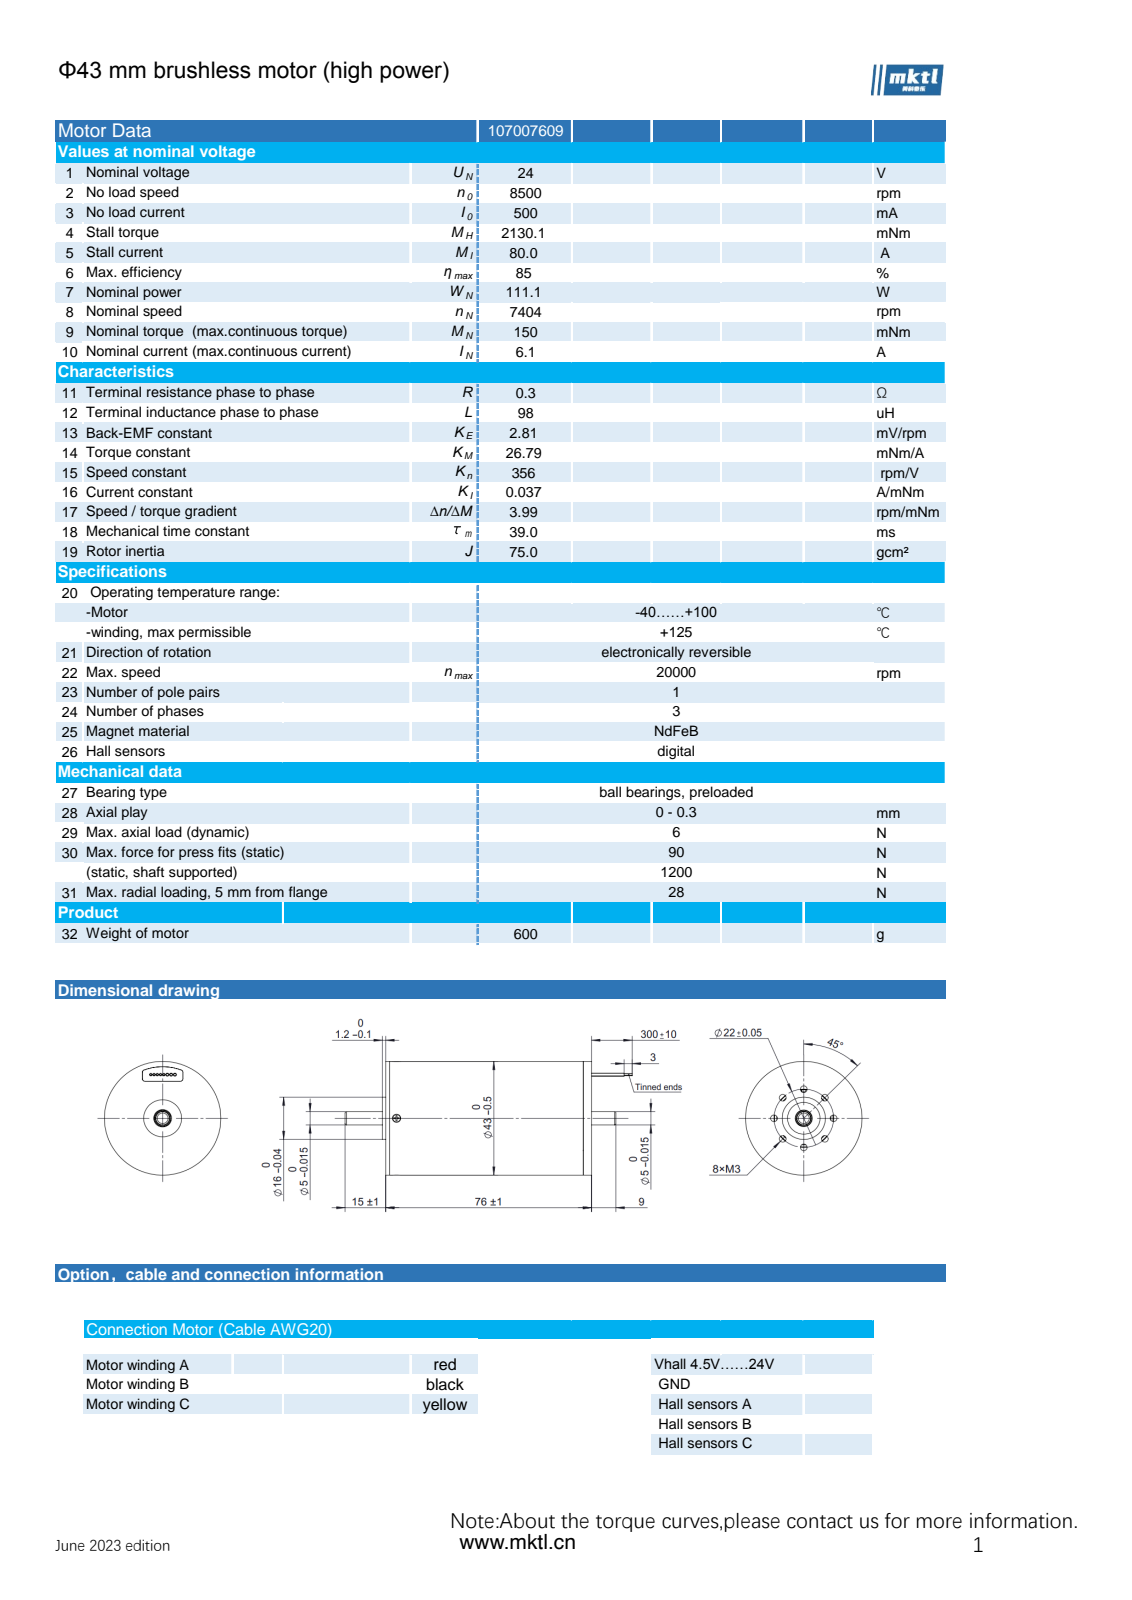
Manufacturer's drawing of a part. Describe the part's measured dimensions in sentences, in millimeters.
The part is named "107007609". Its 3-D file was written by "SolidWorks 2025 (AUTOMOTIVE_DESIGN)". It is 336 solids with 3074 faces: 1143 planar, 1797 cylindrical and 134 other. Overall it measures 106 by 43 by 43 millimeters. Its volume is 100 264 cubic millimeters and its surface area 445 508 square millimeters. Round holes: 9 of diameter 1, 8 of diameter 1.5, 8 of diameter 2.5, 5 of diameter 0.85, 5 of diameter 1.2, 3 of diameter 2.1, 3 of diameter 2.2, 3 of diameter 3, 2 of diameter 3.1, 1 of diameter 6, 1 of diameter 10.5, 1 of diameter 12. Round bosses or shafts: 5 of diameter 0.6, 3 of diameter 4, 3 of diameter 1.6, 3 of diameter 0.8, 3 of diameter 0.5, 2 of diameter 2.8, 2 of diameter 1.4, 2 of diameter 1.3. Partial cylindrical surfaces (rounded edges, fillets, slot ends): 24 of radius 0.1, 21 of radius 1, 3 of radius 0.3, 2 of radius 0.5, 1 of radius 2, 1 of radius 6.1, 1 of radius 6.6, 1 of radius 7.15. The main face-to-face distances are 0.4, 0.6, 0.8, 1, 1.2, 1.4, 1.6, 1.8, 2, 2.2. The hole center spacings are 8.42, 11, 15.56, 20.33, 2, 26.4, 6, 16.
